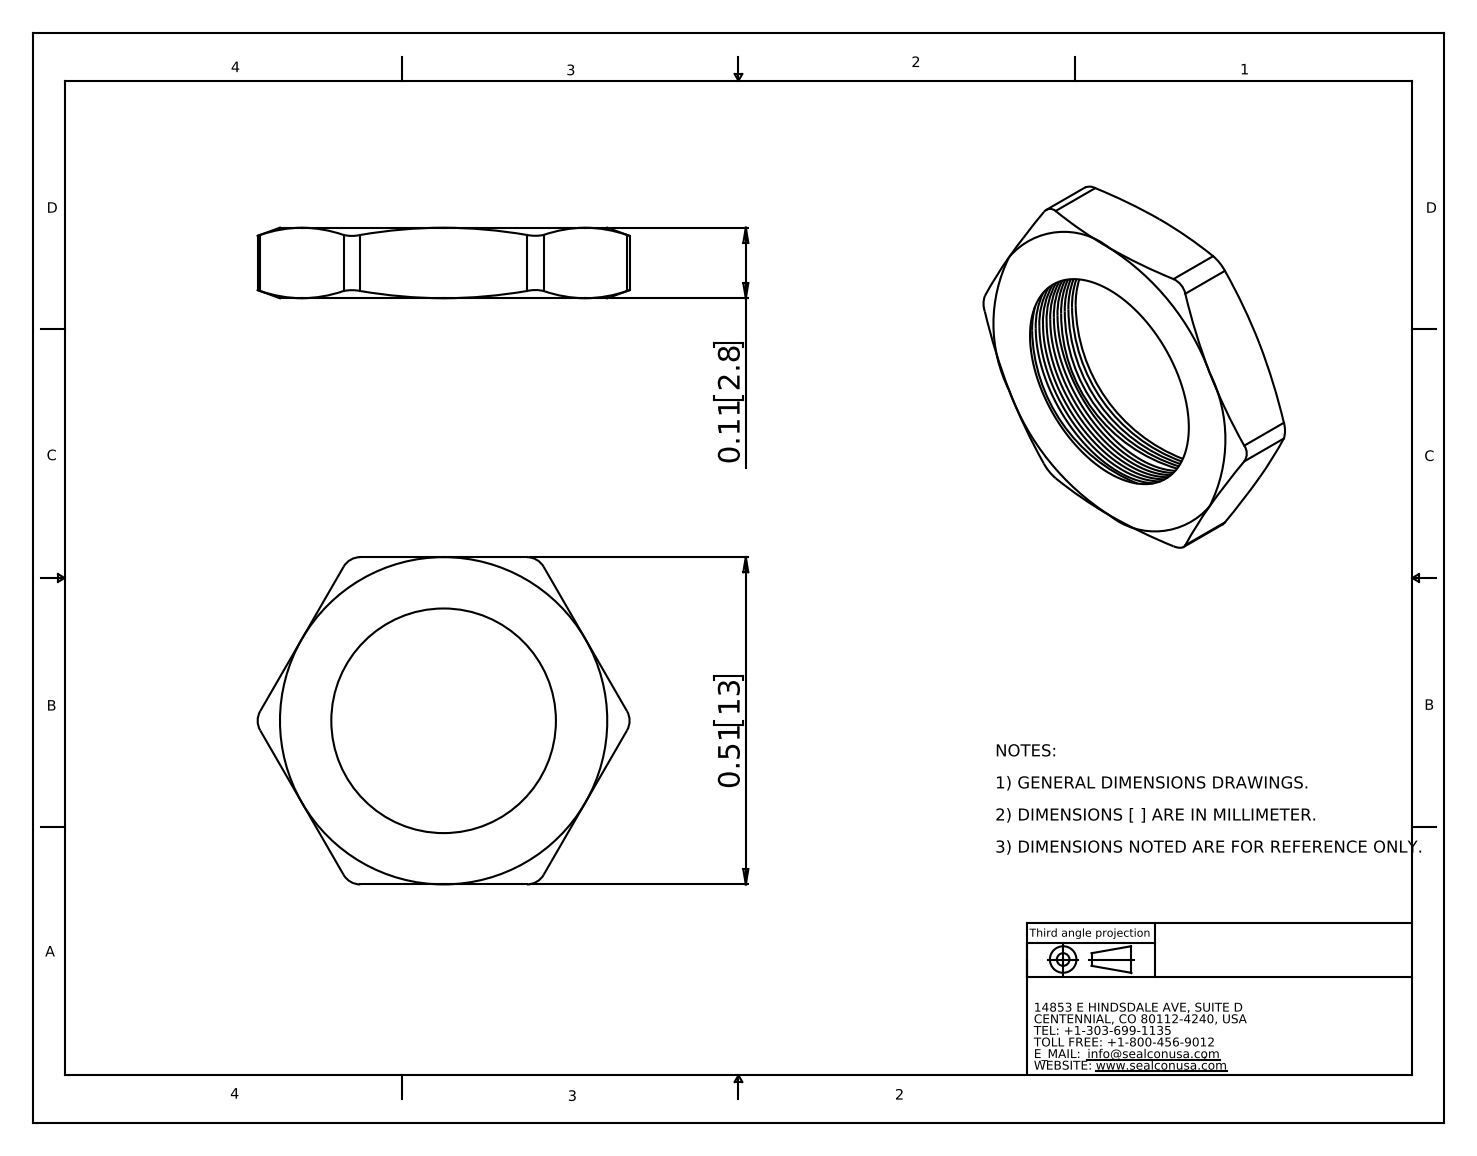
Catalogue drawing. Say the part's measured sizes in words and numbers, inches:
The part is named "NM-10-BR". Its 3-D file was written by "SolidWorks 2007 (CONFIG_CONTROL_DESIGN)". It is 1 solid with 83 faces: 8 planar, 7 cylindrical and 68 other. Overall it measures 0.58 by 0.51 by 0.11 inches. Its volume is 0.013 cubic inches and its surface area 0.681 square inches. Partial cylindrical surfaces (rounded edges, fillets, slot ends): 6 of radius 0.03. The main face-to-face distances are 0.11, 0.51.
